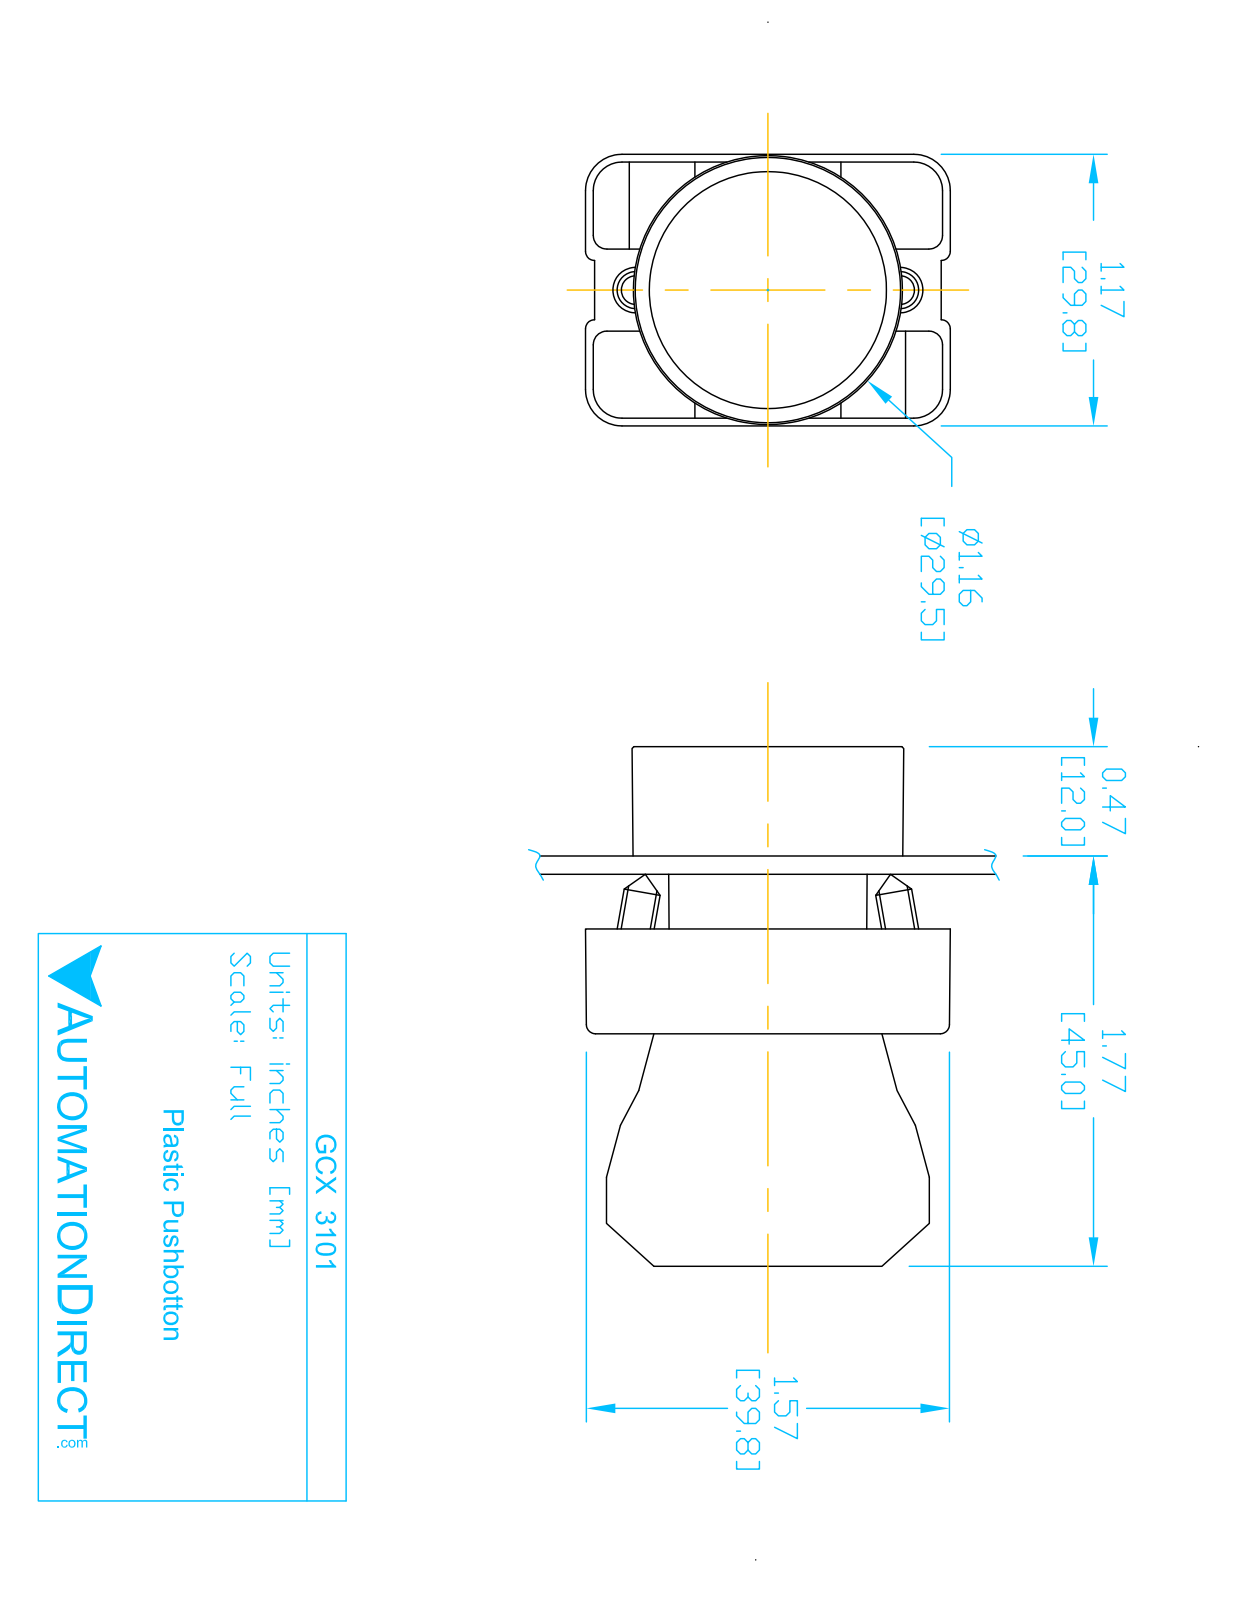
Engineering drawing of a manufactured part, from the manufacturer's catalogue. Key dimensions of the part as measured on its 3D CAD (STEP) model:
Part name (STEP PRODUCT): GCX3101; GCX3101 OPERATOR; ECX3029-2; ecx1030
STEP written by: SolidWorks 2016 (AUTOMOTIVE_DESIGN)
Units: inches
Bodies: 6 solids, 381 faces (222 planar, 132 cylindrical, 27 other)
Overall size (bounding box): 2.217 × 1.581 × 1.177
Volume: 1.741 in³ · Surface area: 27.14 in²
Round holes (diameter × count): ⌀0.079 ×2, ⌀0.124 ×2, ⌀0.13 ×2, ⌀0.087 ×1, ⌀0.197 ×1, ⌀0.878 ×1, ⌀0.888 ×1, ⌀1.024 ×1
Round bosses / shafts (diameter × count): ⌀0.157 ×2, ⌀1.175 ×1, ⌀1.004 ×1, ⌀0.945 ×1, ⌀0.856 ×1, ⌀0.78 ×1
Partial cylindrical surfaces — rounded edges, fillets, slot ends (radius × count): R0.059 ×24, R0.041 ×12, R0.124 ×12, R0.157 ×12, R0.039 ×4, R0.128 ×2, R0.02 ×1, R0.063 ×1
Main face-to-face distances: 0.72, 0.579, 0.033, 0.472, 1.193, 0.031, 0.689, 0.598, 1.161, 1.071
Hole centre spacings: 0.236, 0.544, 0.472, 0.49
